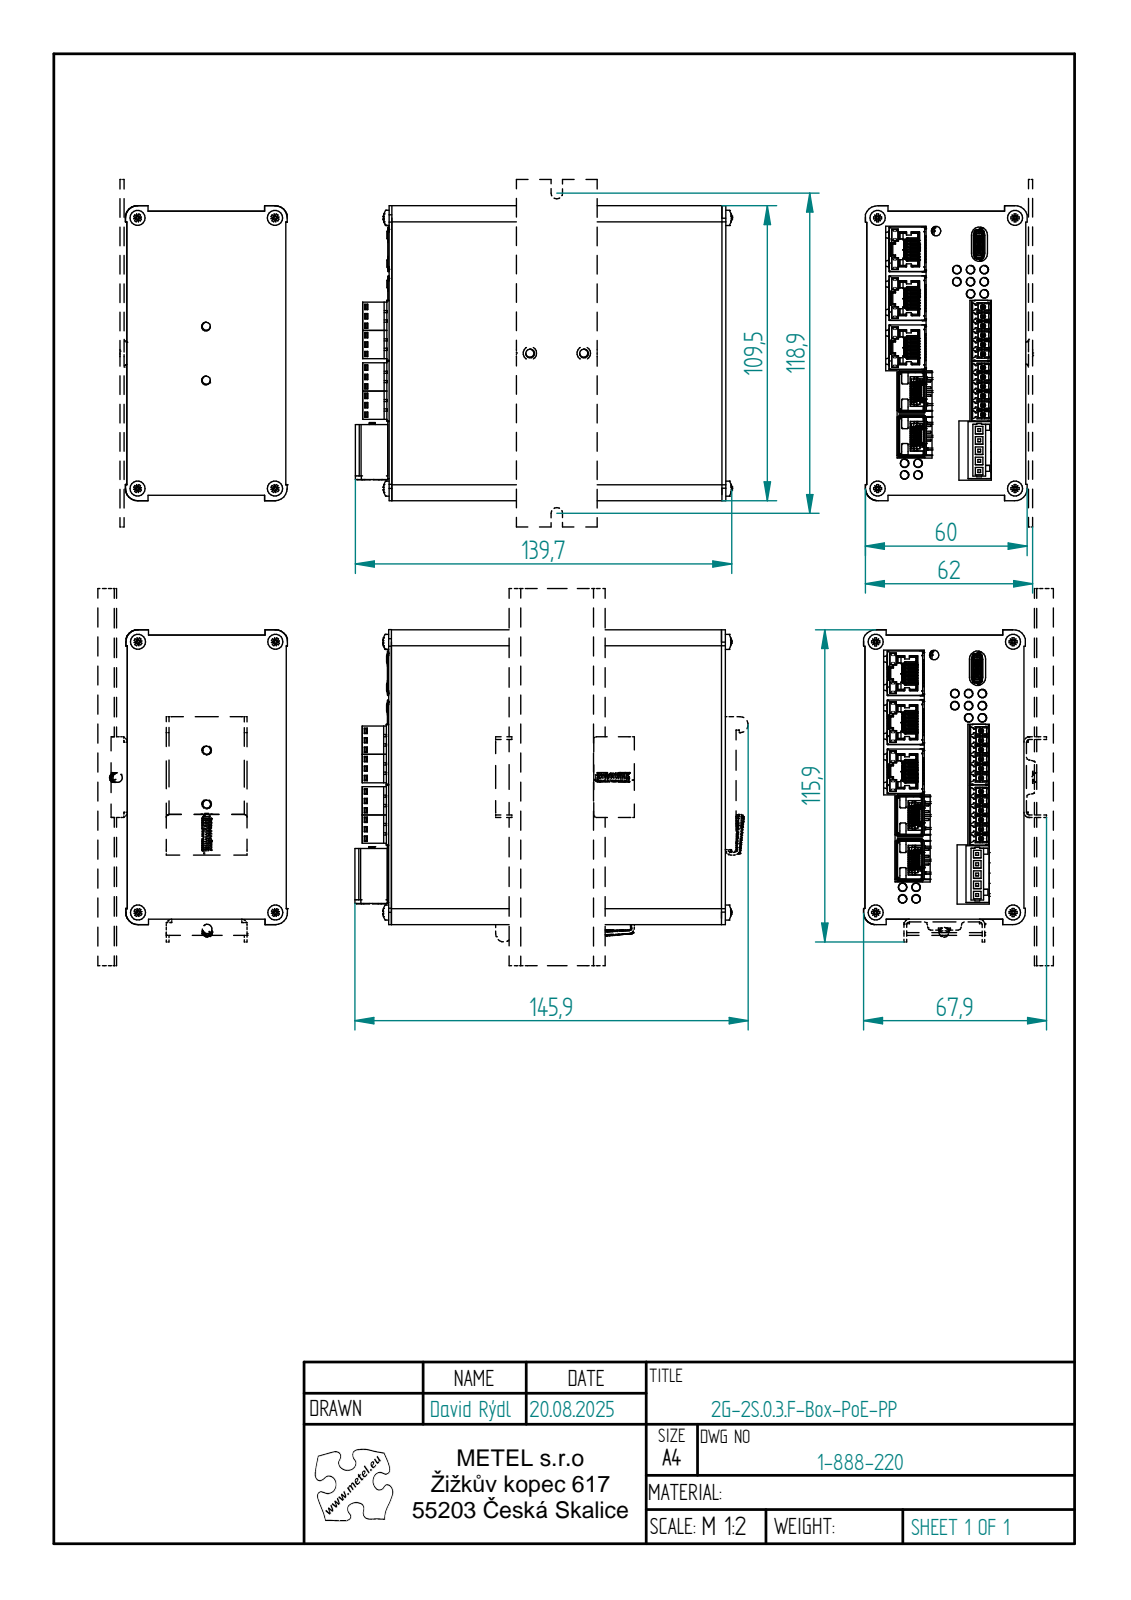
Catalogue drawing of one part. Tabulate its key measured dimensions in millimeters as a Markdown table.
| quantity | value |
| --- | --- |
| part name | 20G-2X03_zakaznik; profil_velky_prekresleny_zakaznik; 2G-2S.0.3; Zadni panylek_velky (+8 more) |
| STEP written by | Solid Edge (AUTOMOTIVE_DESIGN) |
| units | millimeters |
| bodies | 127 solids, 15372 faces (11406 planar, 3248 cylindrical, 718 other) |
| overall size | 145.92 × 140 × 129 |
| volume | 153 796 mm³ |
| surface area | 192 007 mm² |
| round holes (diameter × count) | 1.5 × 17, 1.9 × 12, 2.1 × 12, 2.8 × 12, 3.2 × 12, 3 × 10, 3.5 × 7, 3.54 × 6, 0.45 × 4, 3.4 × 4, 0.4 × 2, 0.5 × 2 |
| round bosses / shafts (diameter × count) | 1.8 × 14, 3 × 12, 5.6 × 4, 2.9 × 4, 2 × 3, 1.78 × 2, 0.6 × 2, 0.45 × 2 |
| partial cylindrical surfaces (radius × count) | 0.1 × 149, 0.25 × 141, 0.2 × 92, 0.15 × 83, 0.25 × 78, 0.24 × 54, 1 × 50, 1.02 × 48 |
| main face-to-face distances | 1.5, 57.5, 1, 4, 59, 2.5, 101.5, 56, 60, 97.5 |
| hole center spacings | 3.5, 7, 10.5, 6.8, 14, 22.51, 4.5, 5.1 |
